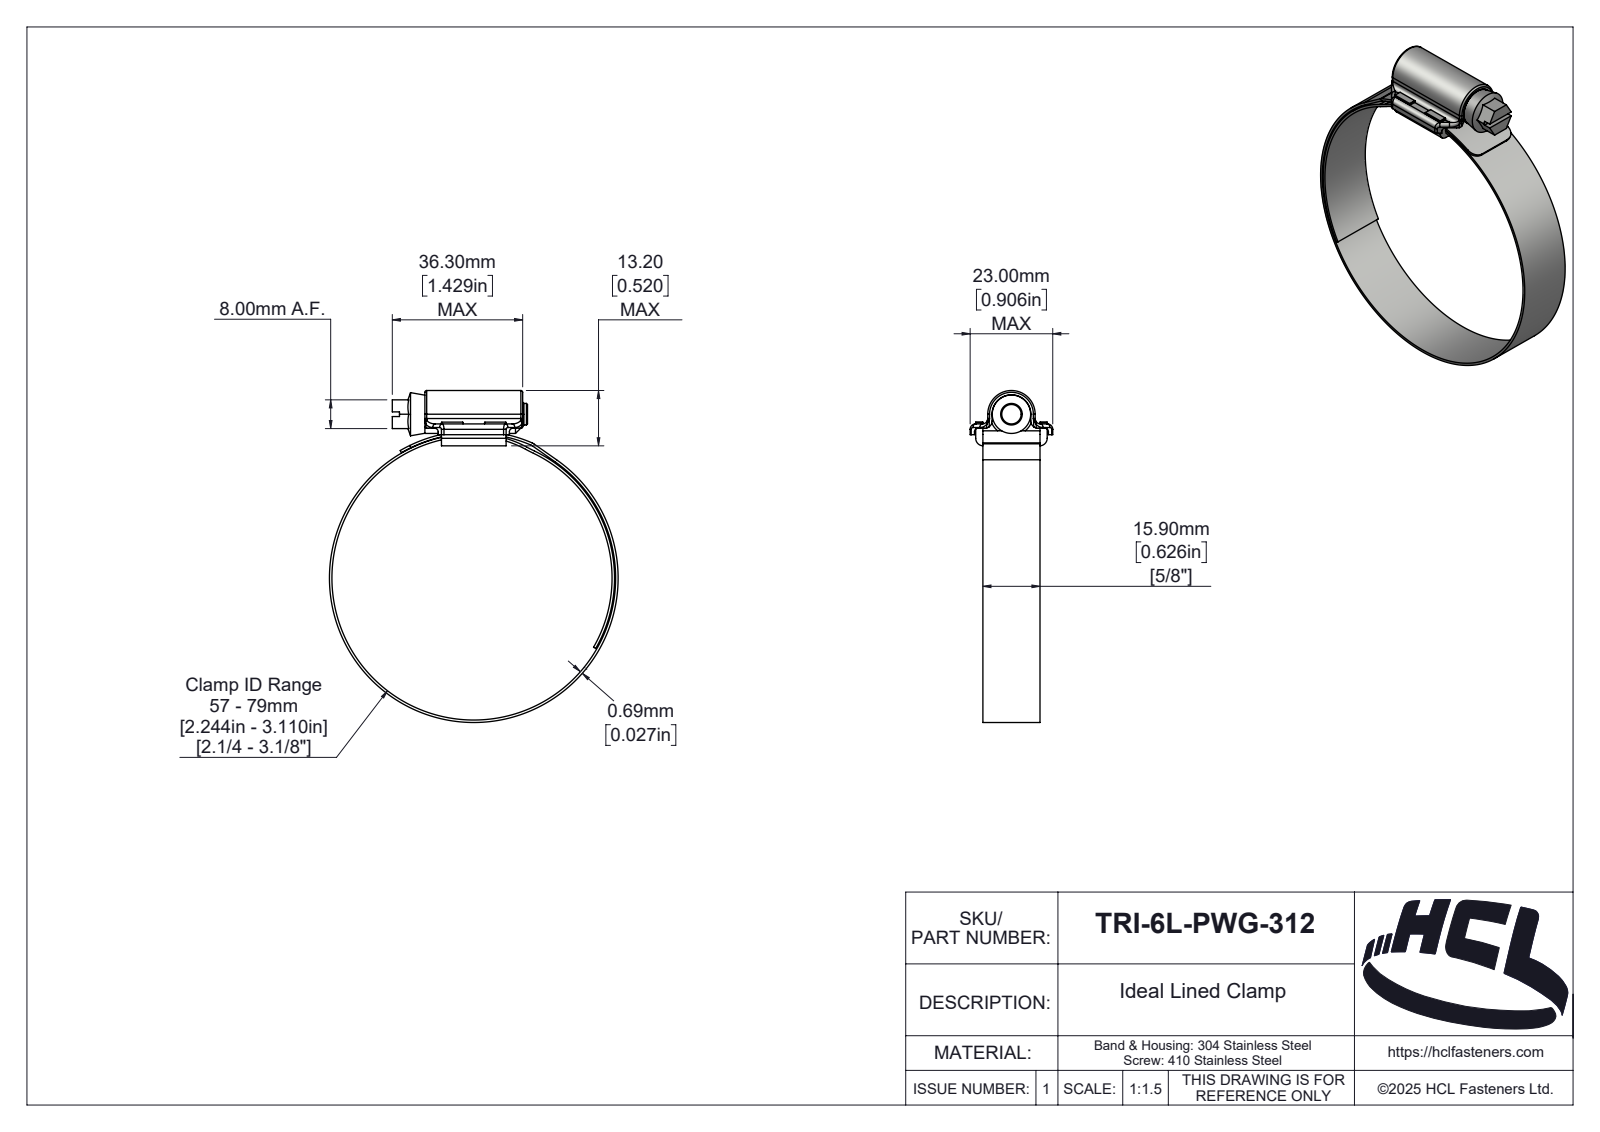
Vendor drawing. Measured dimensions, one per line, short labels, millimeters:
name: TRI-6L-PWG-312
written by: SolidWorks 2025 (AUTOMOTIVE_DESIGN)
unit: mm
bodies: 4 solids, 268 faces (87 planar, 102 cylindrical, 79 other)
size: 92.39 × 80.38 × 23
volume: 9 072 mm³; area: 16 337 mm²
holes: 1× ⌀79
bosses: 1× ⌀80.38, 1× ⌀10.7, 1× ⌀6
rounds: 14× R1, 4× R0.5, 4× R1.5, 3× R2, 2× R0.1, 2× R2.1, 2× R3, 1× R0.46
face distances: 2, 15.9, 17.9, 4.9, 1.2, 0.69, 4.55, 3.35, 15.35, 2.55
